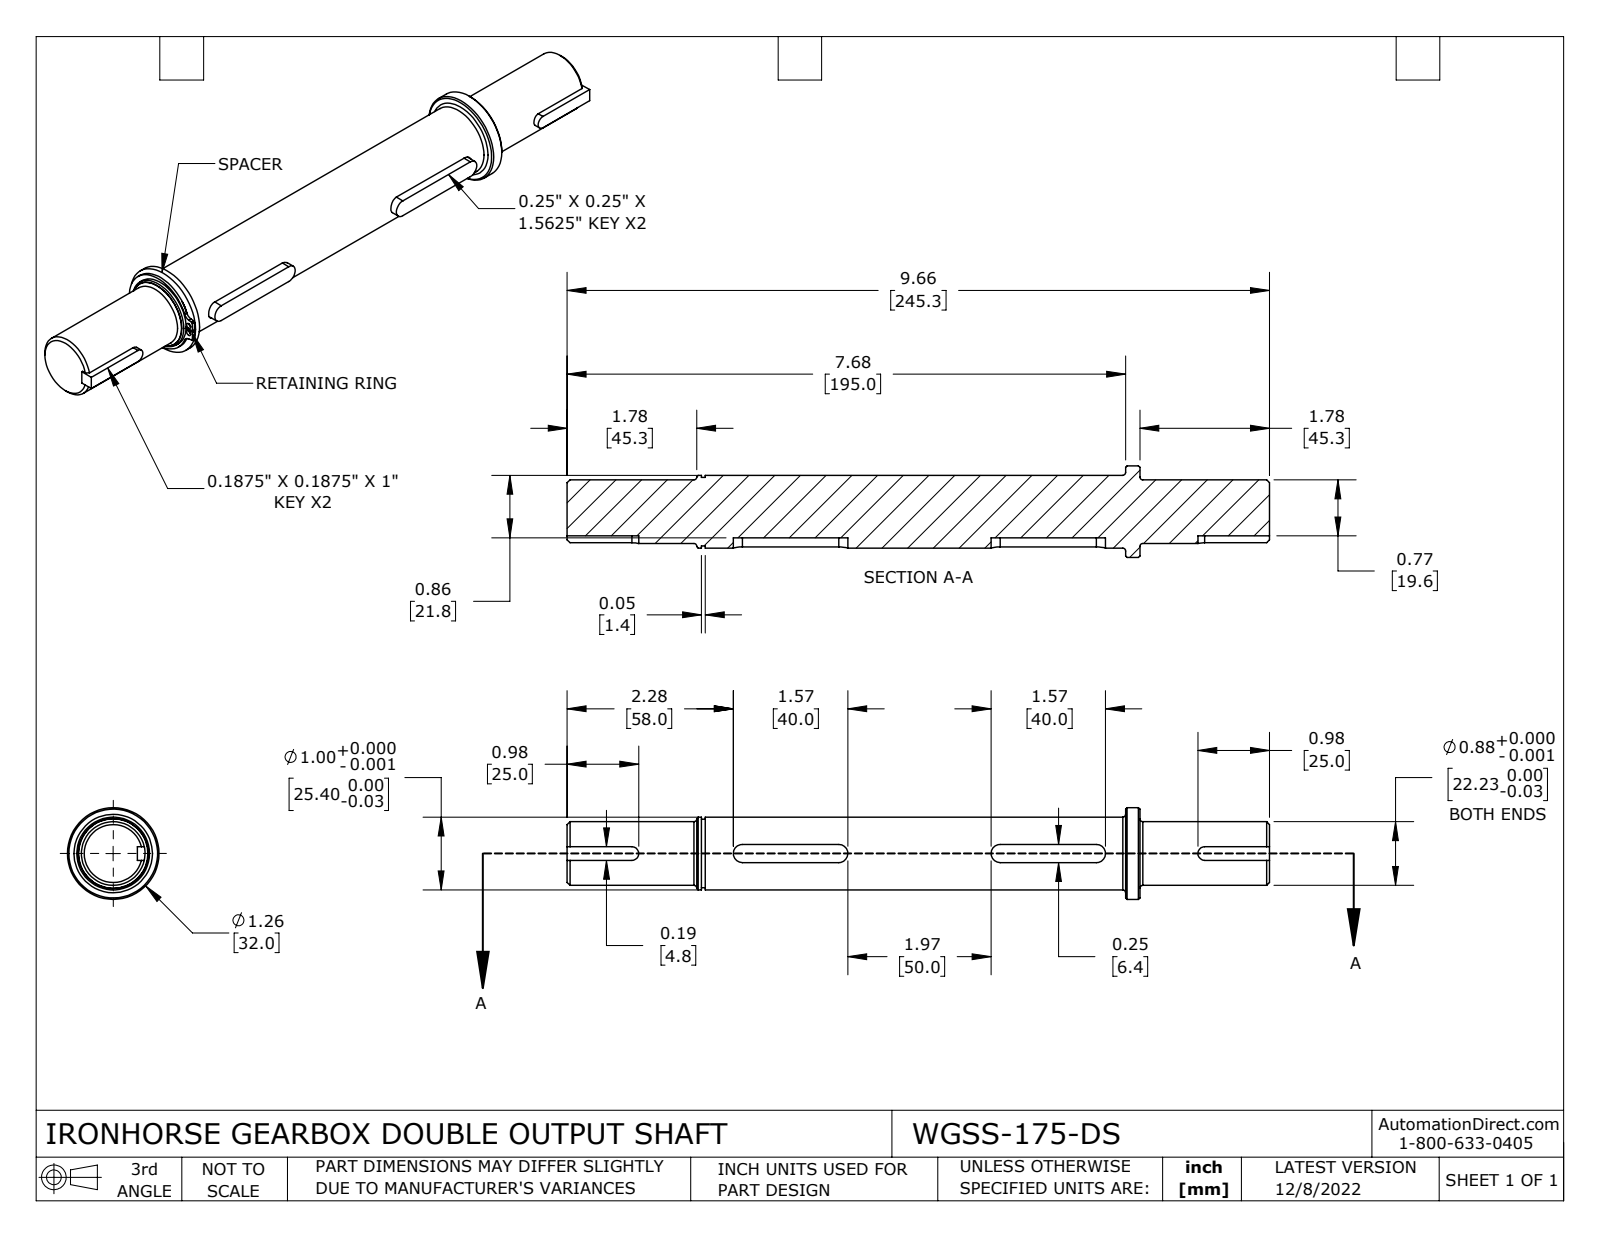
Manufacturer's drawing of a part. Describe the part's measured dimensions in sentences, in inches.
The part is named "WGSS-175-DS". Its 3-D file was written by "SolidWorks 2021 (CONFIG_CONTROL_DESIGN)". It is 7 solids with 108 faces: 47 planar, 45 cylindrical and 16 other. Overall it measures 9.688 by 1.26 by 1.26 inches. Its volume is 7.178 cubic inches and its surface area 39.81 square inches. Round holes: 2 of diameter 0.078, 1 of diameter 0.94, 1 of diameter 1. Round bosses or shafts: 1 of diameter 1.26, 1 of diameter 1.118, 1 of diameter 1, 1 of diameter 0.941, 1 of diameter 0.875. Partial cylindrical surfaces (rounded edges, fillets, slot ends): 6 of radius 0.125, 2 of radius 0.02, 2 of radius 0.094, 2 of radius 0.106. The main face-to-face distances are 0.25, 0.031, 0.219, 0.026, 0.276, 1.978, 7.678, 0.25, 0.187, 7.757. The hole center spacings are 0.57, 0.039, 0.12, 0.541, 0.547.
